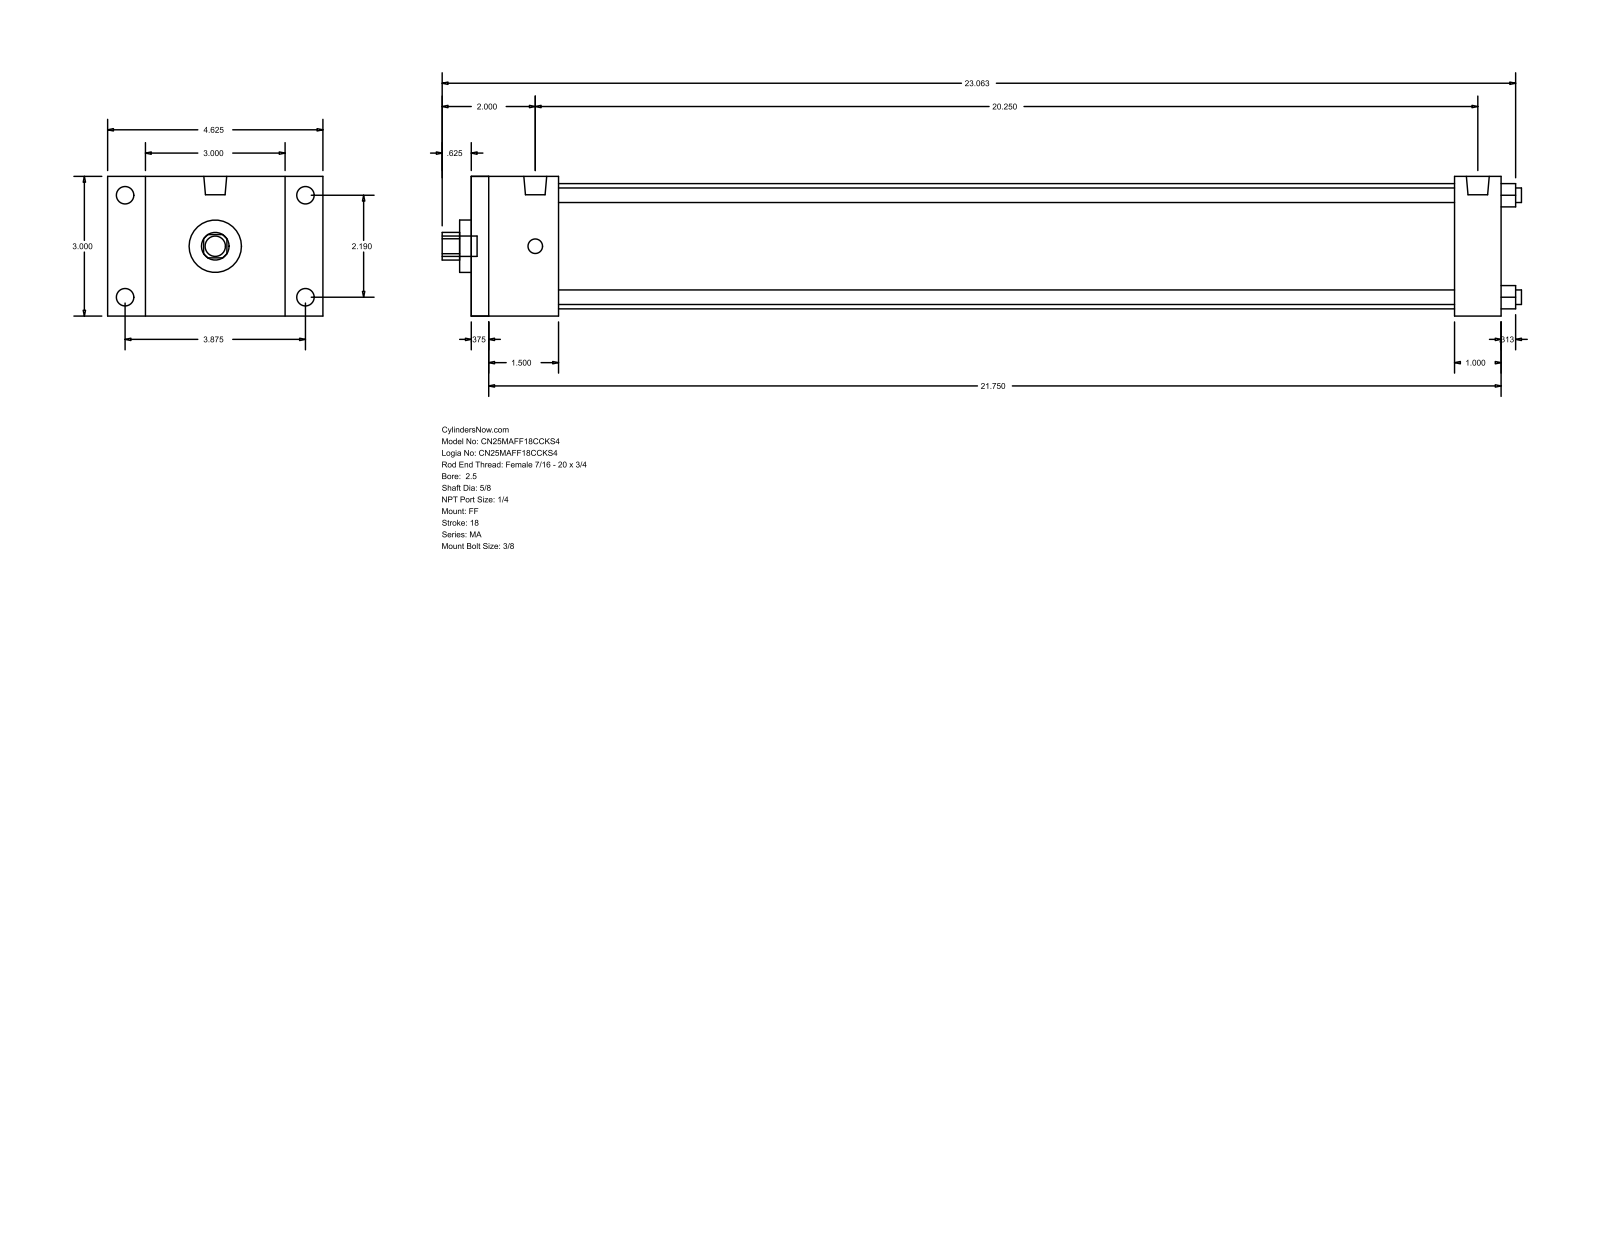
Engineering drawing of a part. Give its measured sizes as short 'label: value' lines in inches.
name: MA_FF__0250_0.625
written by: GSSL Pune (CONFIG_CONTROL_DESIGN)
unit: in
bodies: 0 solids, 92 faces (64 planar, 28 cylindrical, 0 other)
size: 23.187 × 4.625 × 3
holes: 4× ⌀0.313, 1× ⌀0.625, 1× ⌀1.125, 1× ⌀2.69
bosses: 4× ⌀0.375, 4× ⌀0.313, 2× ⌀0.492, 1× ⌀0.437
rounds: 1× R0.297
face distances: 3, 22.125, 0.375, 21.75, 1, 1.875, 21.125, 1.5, 20.75, 19.25
hole spacings: 1.548, 2.19, 3.097
